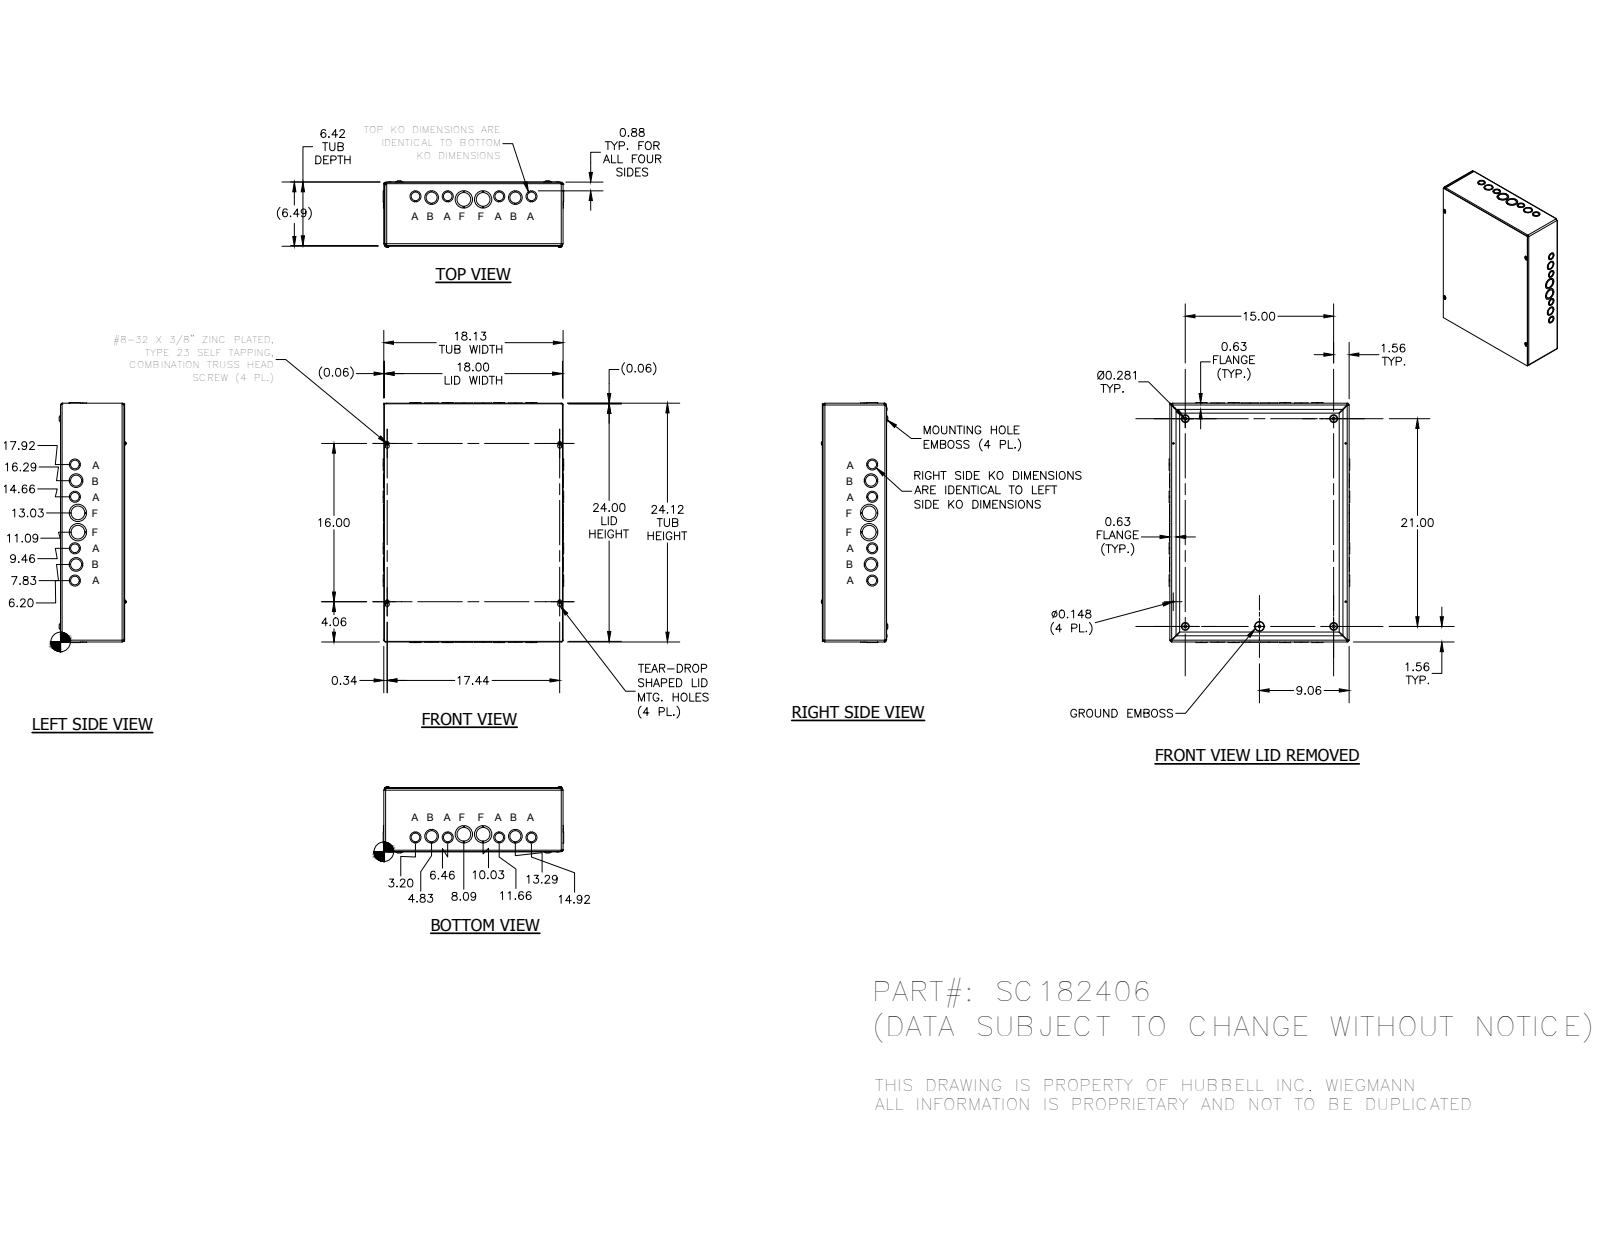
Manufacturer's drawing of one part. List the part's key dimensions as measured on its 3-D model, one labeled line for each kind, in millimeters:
Part name (STEP PRODUCT): SC1824BKP; SC182406WRA; SC1824LID; 34056 (+1 more)
STEP written by: Autodesk Inventor 2014 (AUTOMOTIVE_DESIGN)
Units: millimetres
Bodies: 38 solids, 1255 faces (838 planar, 267 cylindrical, 150 other)
Overall size (bounding box): 615.92 × 463.52 × 170.59
Round holes (diameter × count): ⌀28.57 ×12, ⌀22.22 ×8, ⌀34.92 ×8, ⌀3.76 ×4, ⌀7.62 ×4, ⌀44.45 ×4, ⌀4.19 ×1
Round bosses / shafts (diameter × count): ⌀4.57 ×8, ⌀9.75 ×4, ⌀4.17 ×4, ⌀5.8 ×1
Partial cylindrical surfaces — rounded edges, fillets, slot ends (radius × count): R3.17 ×12, R4.75 ×8, R1.4 ×4, R1.57 ×4, R2.38 ×4, R2.97 ×4, R3.15 ×4, R3.96 ×4
Main face-to-face distances: 1.88, 163, 161.12, 1.57, 164.88, 458.8, 1.58, 460.37, 457.23, 612.78
Hole centre spacings: 41.52, 42.15, 82.94, 91.03, 132.17, 173.51, 214.88, 470.92
